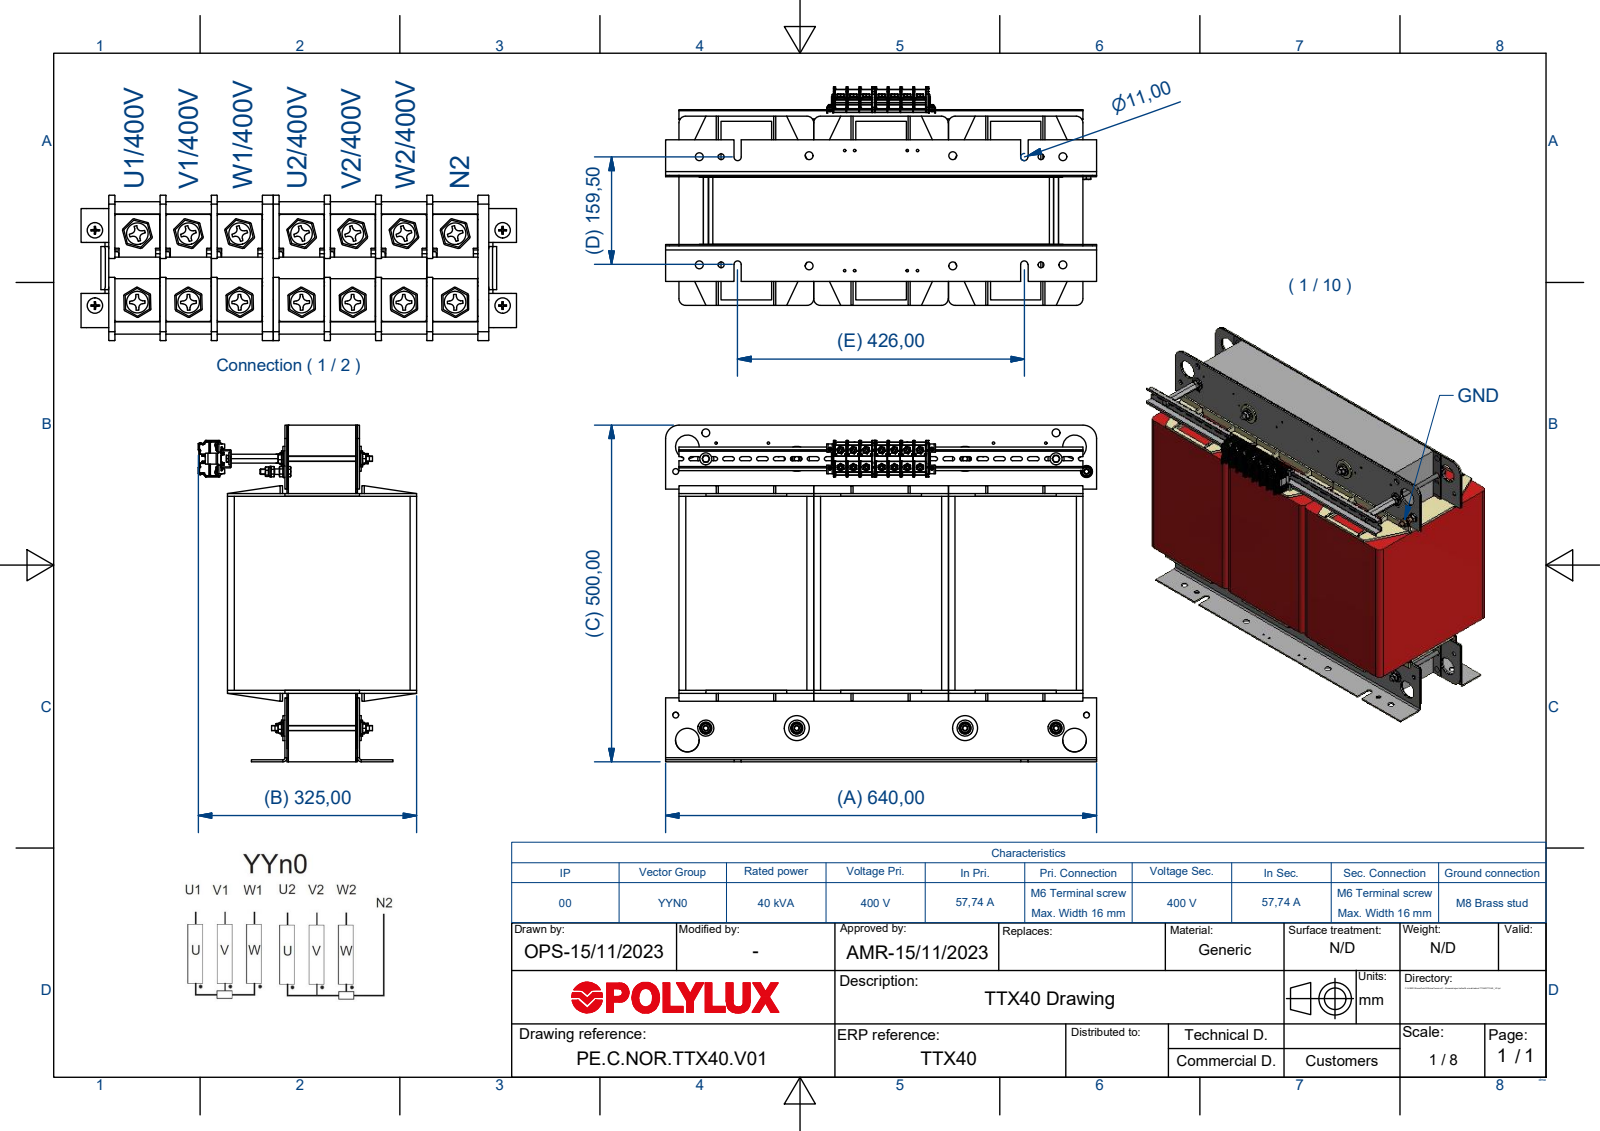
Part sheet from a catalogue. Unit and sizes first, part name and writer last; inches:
Units: inches
Overall size (bounding box): 25.197 × 19.685 × 12.366
Round holes (diameter × count): ⌀0.472 ×22, ⌀0.177 ×20, ⌀0.138 ×18, ⌀0.197 ×14, ⌀0.209 ×14, ⌀0.213 ×14, ⌀0.315 ×14, ⌀0.354 ×10, ⌀0.453 ×10, ⌀0.262 ×8, ⌀0.331 ×8, ⌀0.335 ×8
Round bosses / shafts (diameter × count): ⌀0.394 ×14, ⌀0.362 ×14, ⌀0.303 ×14, ⌀0.23 ×14, ⌀0.63 ×8, ⌀0.583 ×8, ⌀0.315 ×8, ⌀0.154 ×4
Partial cylindrical surfaces — rounded edges, fillets, slot ends (radius × count): R0.006 ×1208, R0.02 ×120, R0.004 ×80, R0.059 ×58, R0.118 ×50, R0.061 ×44, R0.197 ×20, R0.039 ×18
Main face-to-face distances: 7.874, 3.937, 4.094, 0.157, 7.717, 0.079, 4.016, 15.748, 5.906, 0.138
Hole centre spacings: 13.131, 8.11, 3.071, 3.733, 9.843, 16.621, 0.591, 0.938
Volume: 3 733 in³ · Surface area: 7 704 in²
Bodies: 142 solids, 8153 faces (2799 planar, 3256 cylindrical, 2098 other)
Part name (STEP PRODUCT): TTX40_V2
STEP written by: Autodesk Inventor 2018 (AUTOMOTIVE_DESIGN)
